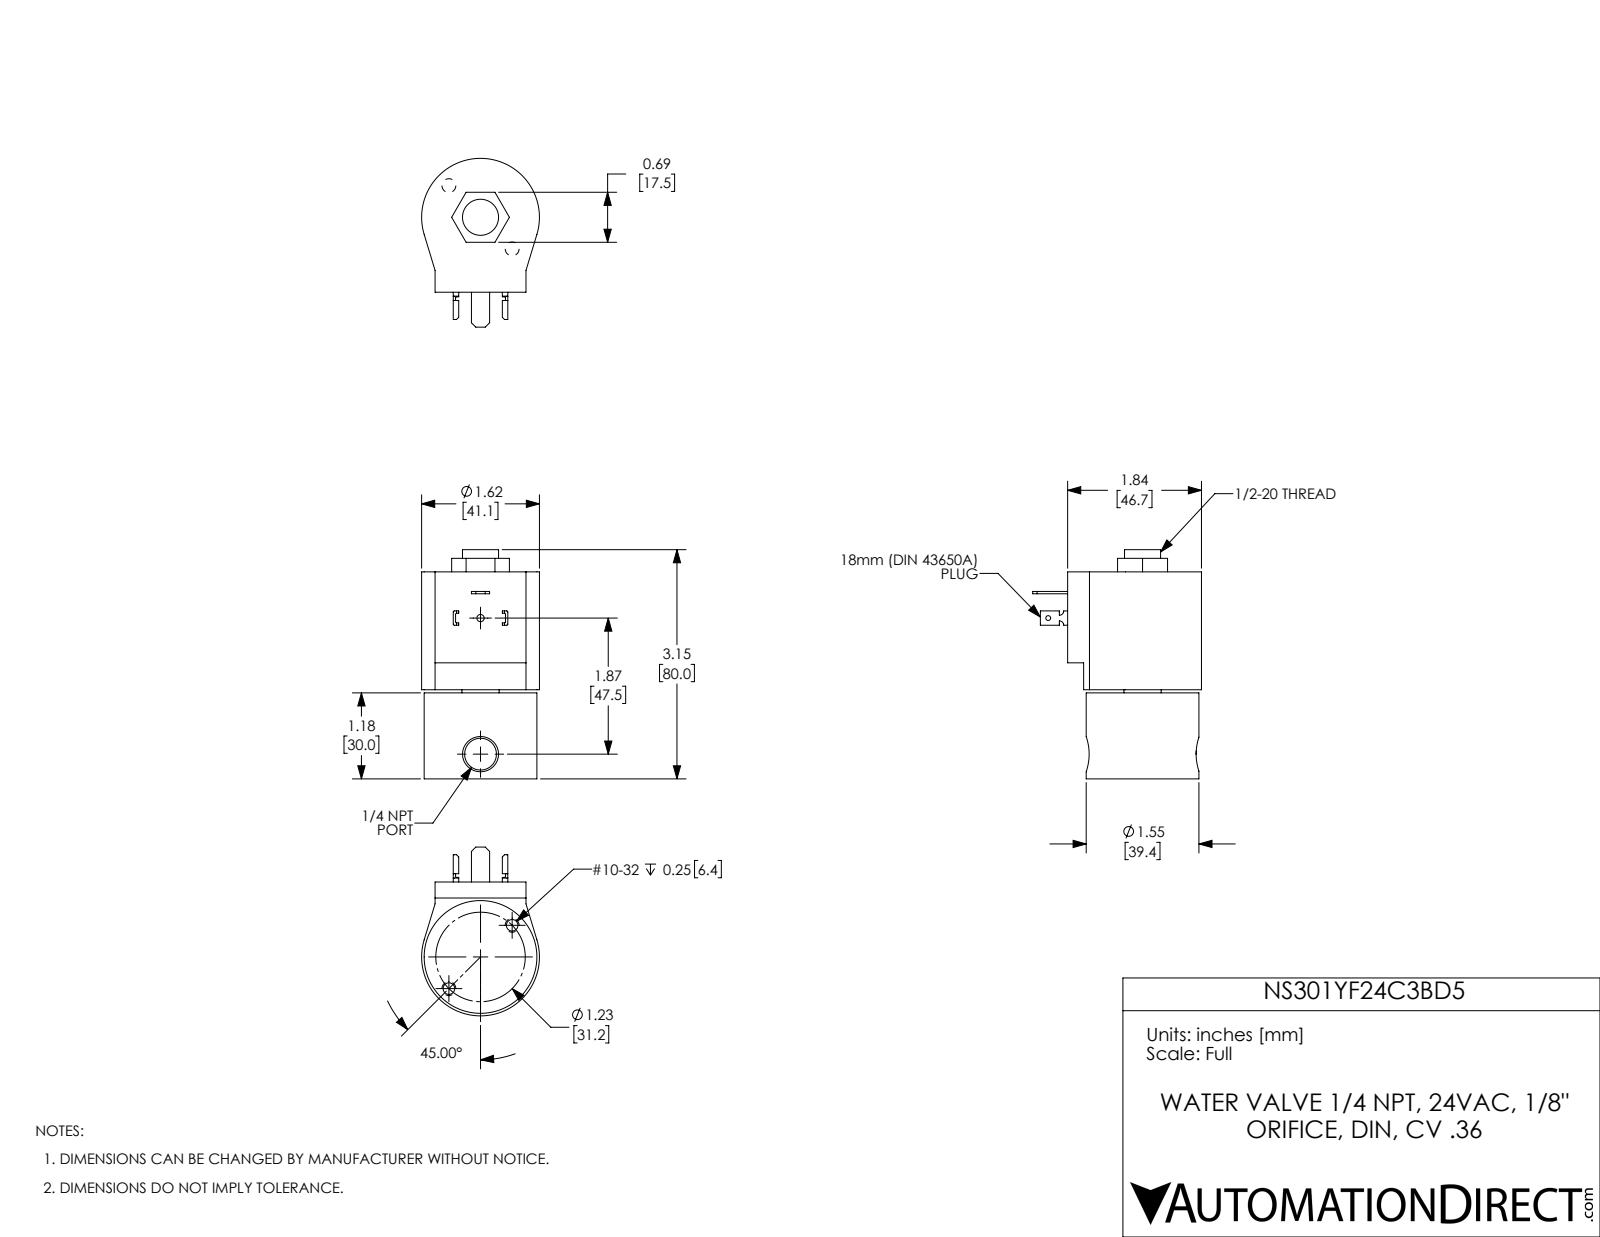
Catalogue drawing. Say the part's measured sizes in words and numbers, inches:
The part is named "NS301YF24C3BD5". Its 3-D file was written by "SolidWorks 2017 (AUTOMOTIVE_DESIGN)". It is 6 solids with 130 faces: 73 planar, 49 cylindrical and 8 other. Overall it measures 3.15 by 2.32 by 1.62 inches. Its volume is 6.027 cubic inches and its surface area 33.08 square inches. Round holes: 2 of diameter 0.159, 1 of diameter 0.067, 1 of diameter 0.1, 1 of diameter 0.437, 1 of diameter 0.496, 1 of diameter 0.512, 1 of diameter 1.155. Round bosses or shafts: 1 of diameter 1.55. Partial cylindrical surfaces (rounded edges, fillets, slot ends): 8 of radius 0.015, 2 of radius 0.06, 1 of radius 0.81. The main face-to-face distances are 2.845, 1.182, 1.663, 1.225, 0.043, 1.62, 1.287, 0.106, 0.062, 1.558. The hole center spacings are 0.615, 1.23, 1.87.
